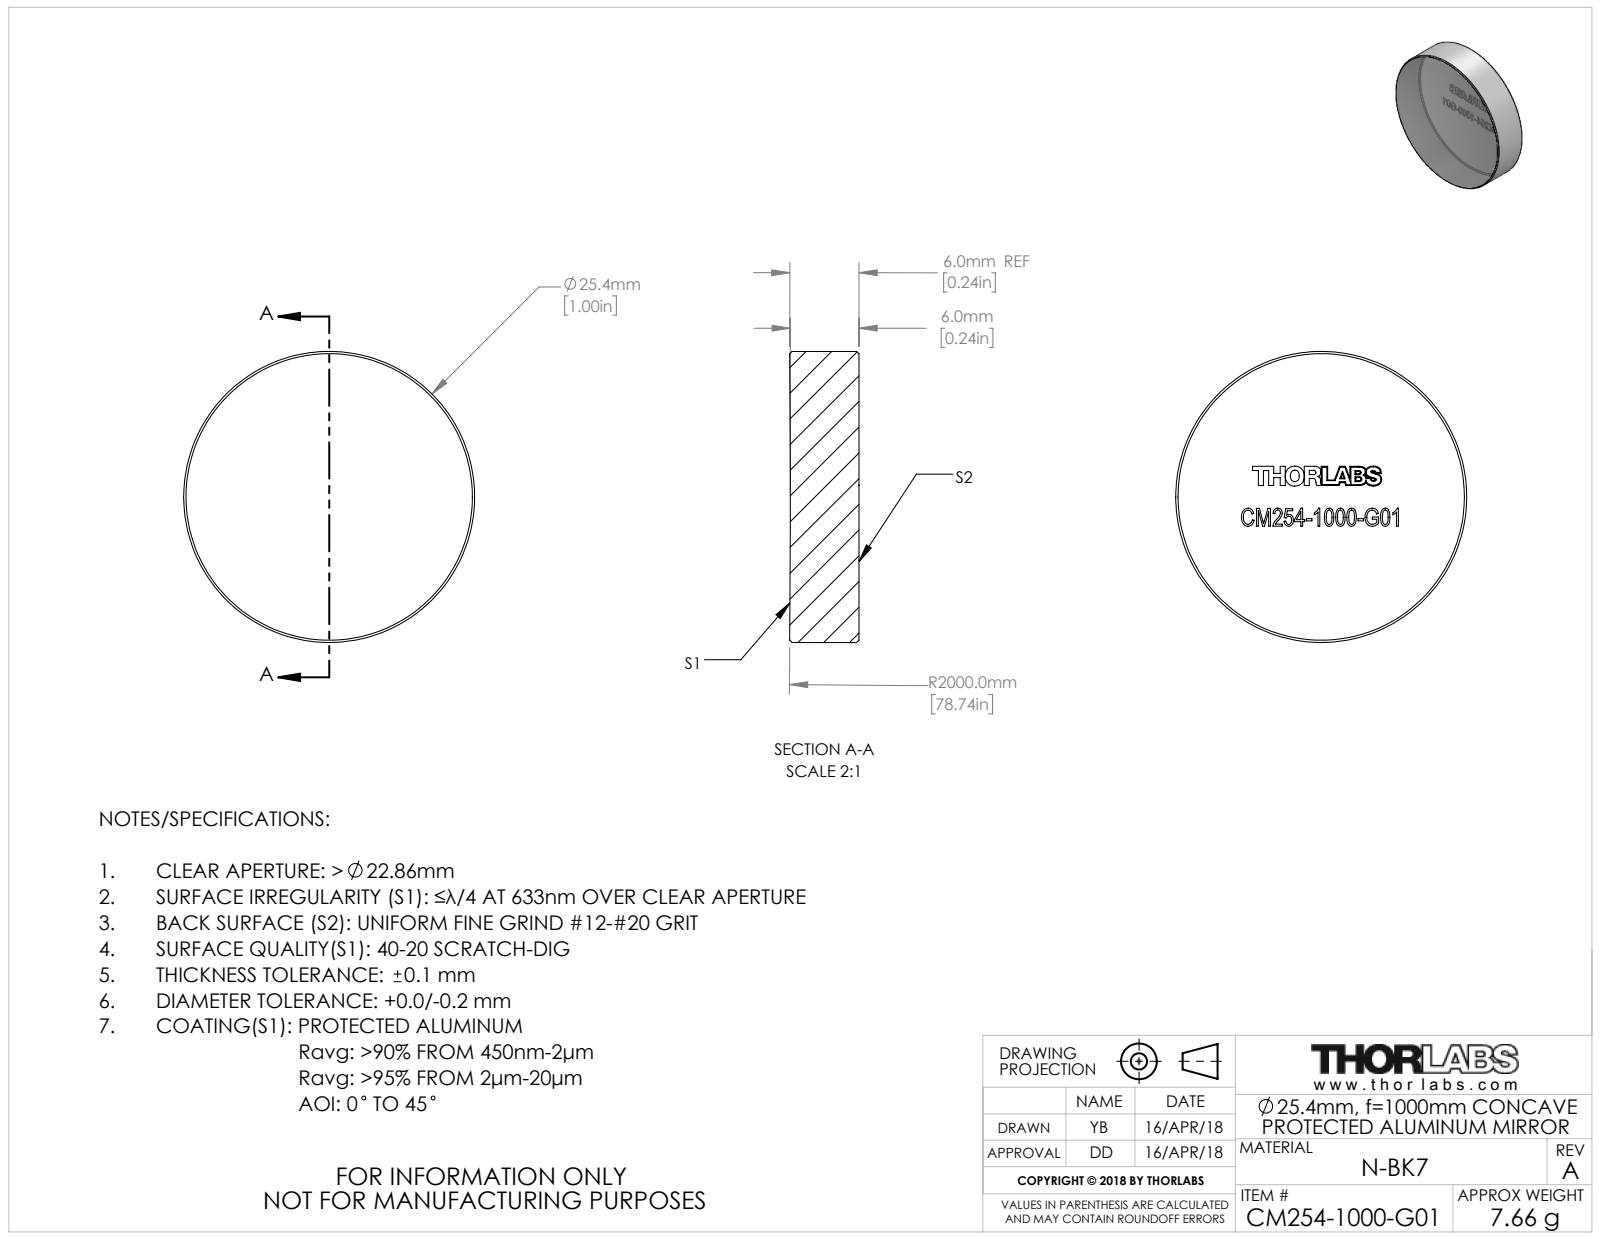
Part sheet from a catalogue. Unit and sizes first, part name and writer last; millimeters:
Units: millimetres
Overall size (bounding box): 25.4 × 25.4 × 6.04
Round bosses / shafts (diameter × count): ⌀25.4 ×1
Volume: 3 047 mm³ · Surface area: 1 477 mm²
Bodies: 1 solid, 43 faces (35 planar, 2 cylindrical, 6 other)
Part name (STEP PRODUCT): TTN153315-E0W
STEP written by: SolidWorks 2018 (CONFIG_CONTROL_DESIGN)
